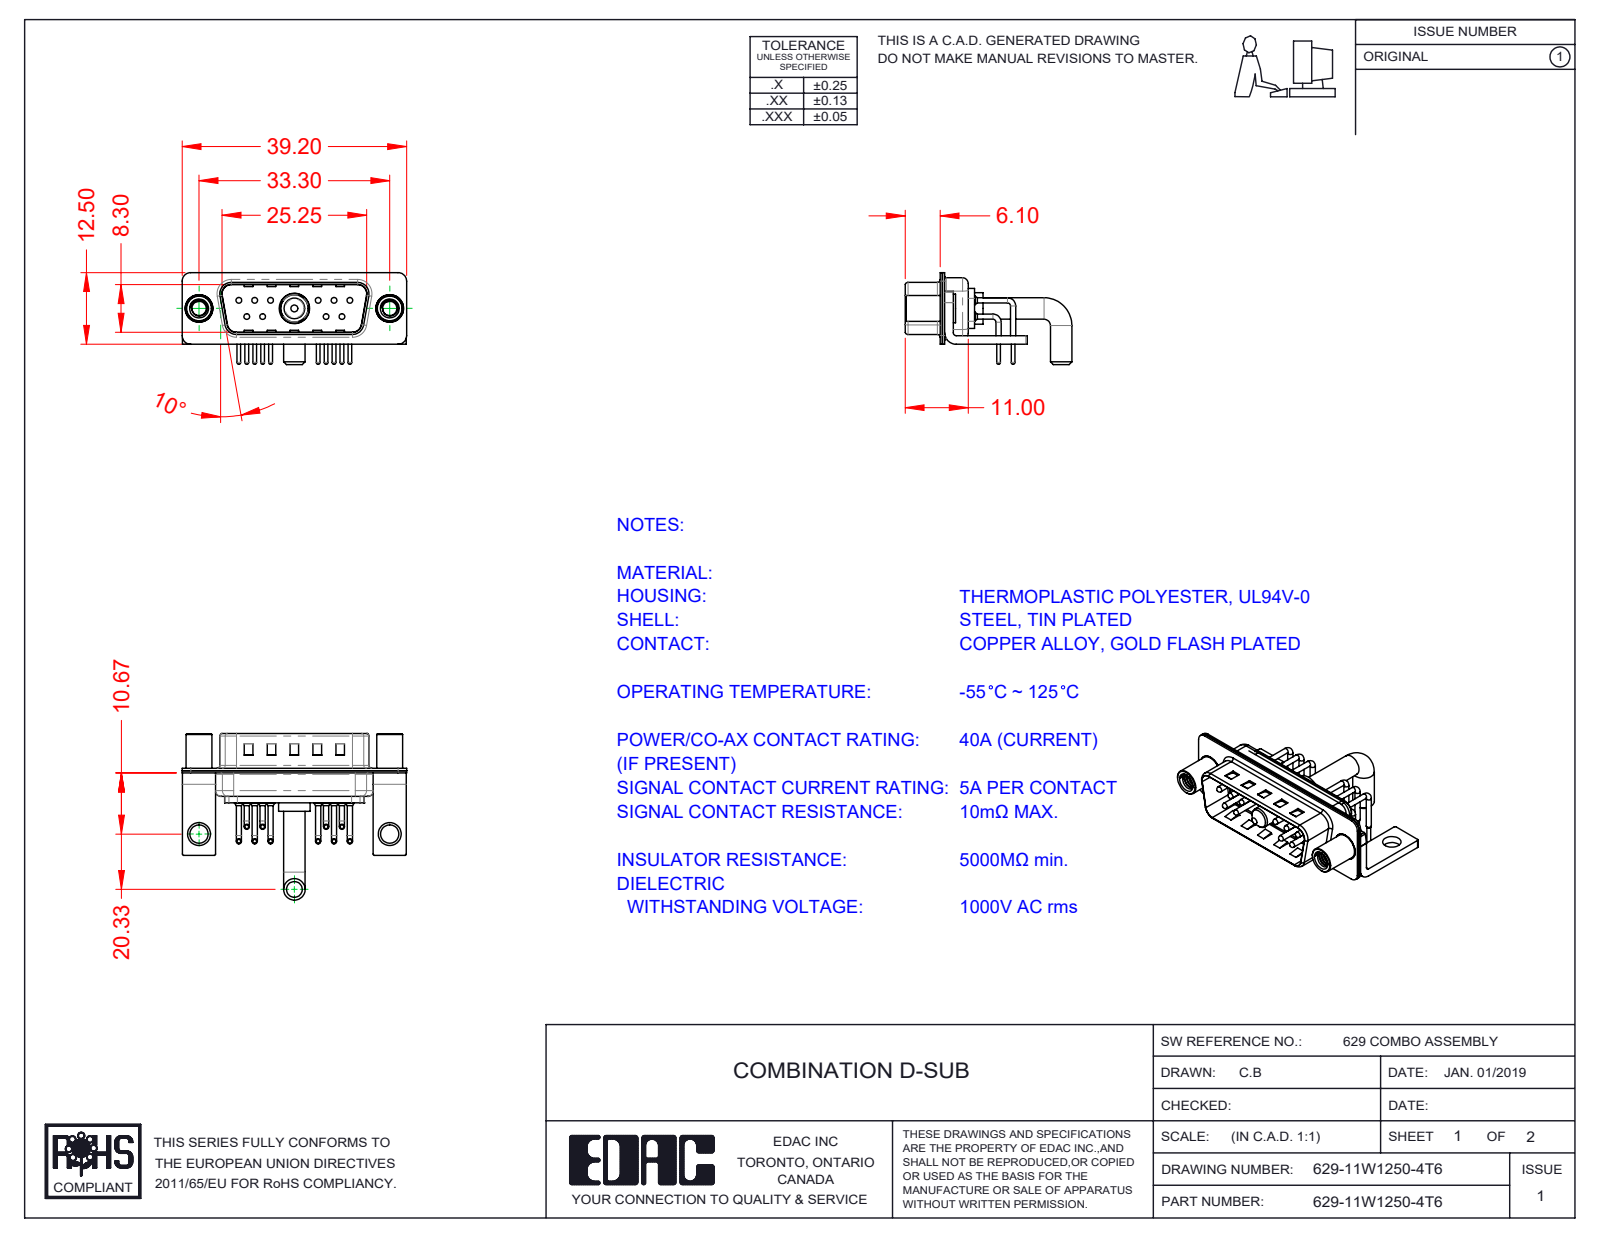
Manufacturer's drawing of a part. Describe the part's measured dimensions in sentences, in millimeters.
The part is named "Power Pin_Ext 40A RA; 629Combo Contact Row 1; 629Combo Stabilizer Bracket; 629Combo Housing_11W1 (+5 more)". Its 3-D file was written by "SolidWorks 2020 (CONFIG_CONTROL_DESIGN)". It is 19 solids with 1594 faces: 820 planar, 590 cylindrical and 184 other. Overall it measures 39.2 by 29.11 by 16.05 millimeters. Its volume is 2 599 cubic millimeters and its surface area 6 286 square millimeters. Round holes: 10 of diameter 0.75, 10 of diameter 1.6, 10 of diameter 2, 2 of diameter 2.5, 2 of diameter 3.2, 2 of diameter 4, 2 of diameter 4.8, 1 of diameter 4.85, 1 of diameter 5.3. Round bosses or shafts: 20 of diameter 0.9, 10 of diameter 1.5, 10 of diameter 1, 10 of diameter 0.65, 2 of diameter 5, 2 of diameter 4.9, 2 of diameter 4.5, 2 of diameter 3.75. Partial cylindrical surfaces (rounded edges, fillets, slot ends): 16 of radius 0.25, 16 of radius 1.5, 13 of radius 2, 10 of radius 1.01, 9 of radius 0.5, 8 of radius 1.6, 7 of radius 1, 4 of radius 0.6. The main face-to-face distances are 0.4, 0.8, 1.5, 9.5, 9.1, 8.7, 9.9, 0.6, 1.9, 2.1. The hole center spacings are 3.16, 2.77, 13.85, 11.08, 16.62, 5.03, 5.04, 5.54.
